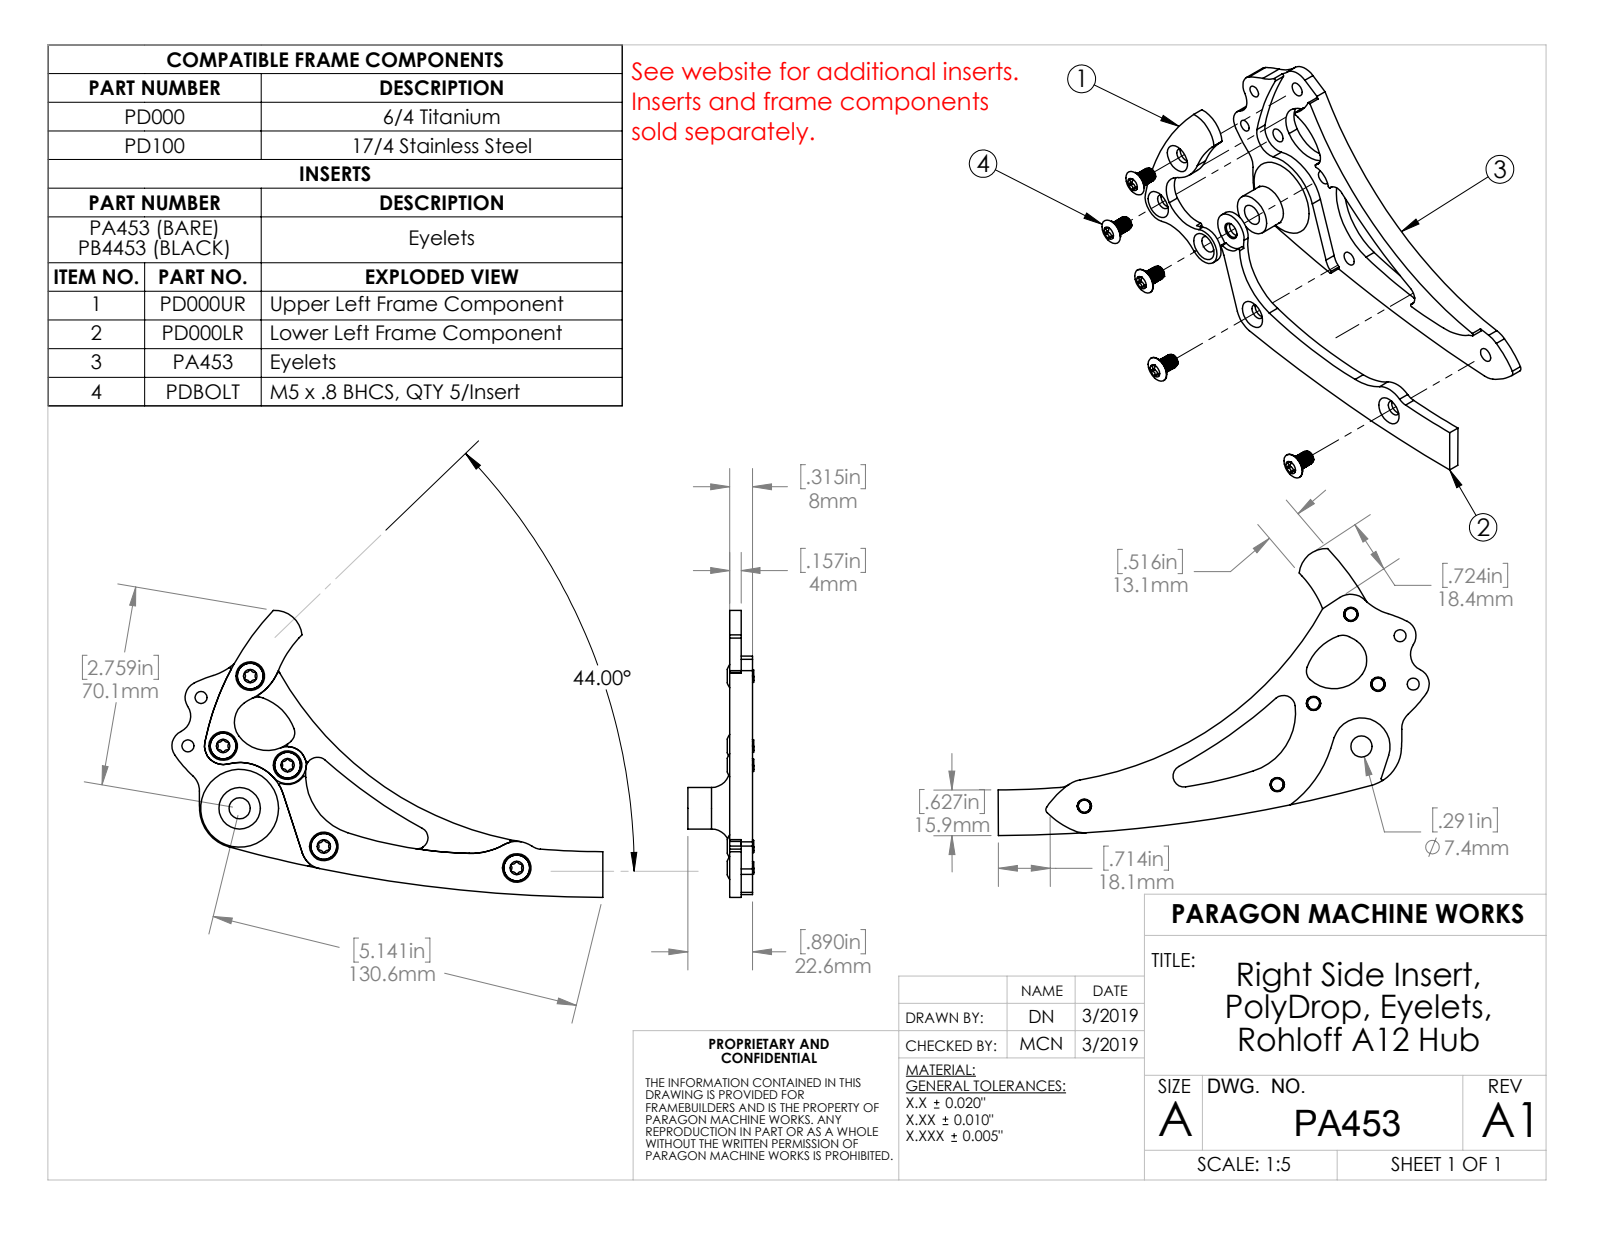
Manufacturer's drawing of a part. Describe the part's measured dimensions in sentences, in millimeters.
The part is named "PA453". Its 3-D file was written by "SolidWorks 2019 (AUTOMOTIVE_DESIGN)". It is 1 solid with 85 faces: 10 planar, 73 cylindrical and 2 other. Overall it measures 133.88 by 83.25 by 22.6 millimeters. Its volume is 23 685 cubic millimeters and its surface area 13 216 square millimeters. Round holes: 5 of diameter 5, 2 of diameter 4.2, 1 of diameter 7.4. Round bosses or shafts: 1 of diameter 14.48. Partial cylindrical surfaces (rounded edges, fillets, slot ends): 9 of radius 0.5, 2 of radius 5.59, 2 of radius 6.5, 2 of radius 7, 2 of radius 18, 2 of radius 30.71, 2 of radius 44.03, 1 of radius 1.5. The main face-to-face distances are 4, 8, 3.5, 0.5, 4.5, 22.6, 19.1, 18.6, 14.6, 26. The hole center spacings are 22.5, 12.3, 17.5, 18.6, 18.73, 23.48, 26.16, 28.31.
